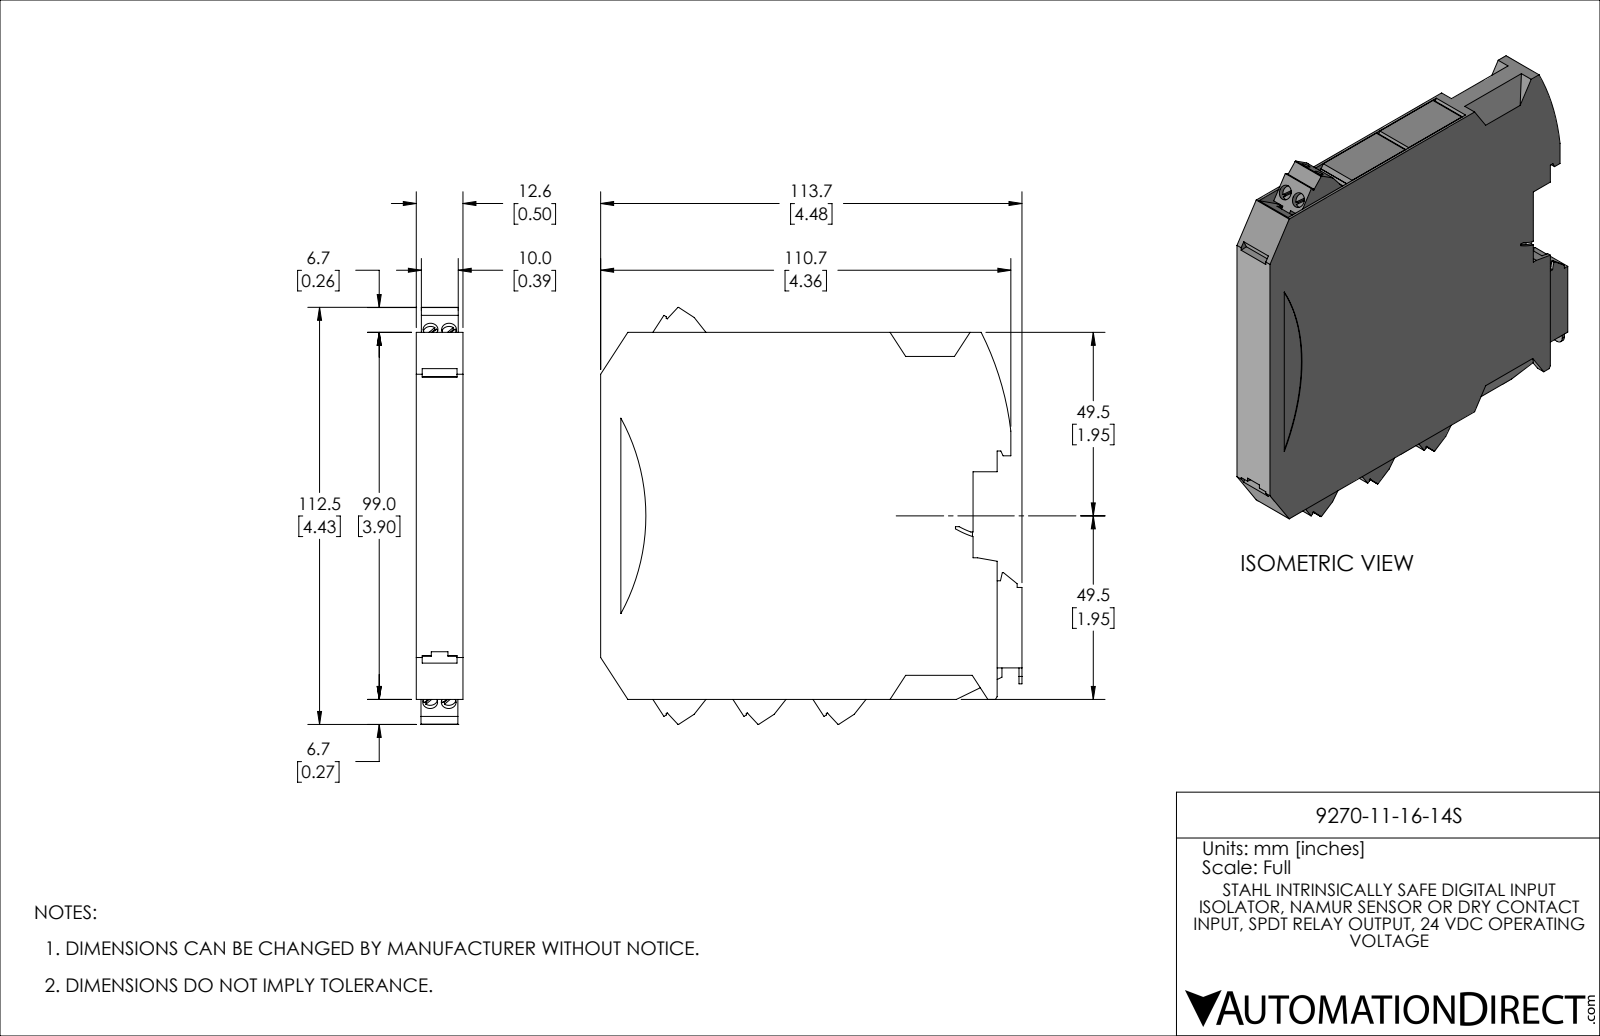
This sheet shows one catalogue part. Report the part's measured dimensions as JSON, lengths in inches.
{"part_name": "9270-11-16-14S", "step_written_by": "SolidWorks 2021 (AUTOMOTIVE_DESIGN)", "units": "inches", "bodies": {"solids": 1, "faces": 898, "planar": 805, "cylindrical": 85, "other": 8}, "overall_size": [4.476, 4.429, 0.496], "volume_in3": 7.675, "surface_area_in2": 62.13, "round_holes": [[0.06, 8], [0.088, 8], [0.118, 8], [0.157, 8]], "round_bosses_or_shafts": [[0.11, 6]], "partial_cylinders_radius": [[0.118, 14], [0.114, 8], [0.055, 6], [0.008, 4], [0.02, 2], [0.059, 2], [0.079, 2], [0.098, 2]], "face_to_face_distances": [0.496, 0.03, 0.467, 0.713, 0.392, 0.465, 0.437, 0.054, 0.442, 0.024], "hole_center_spacings": [0.197, 0.713, 0.463, 0.74, 0.849, 0.872, 0.503, 0.504]}
